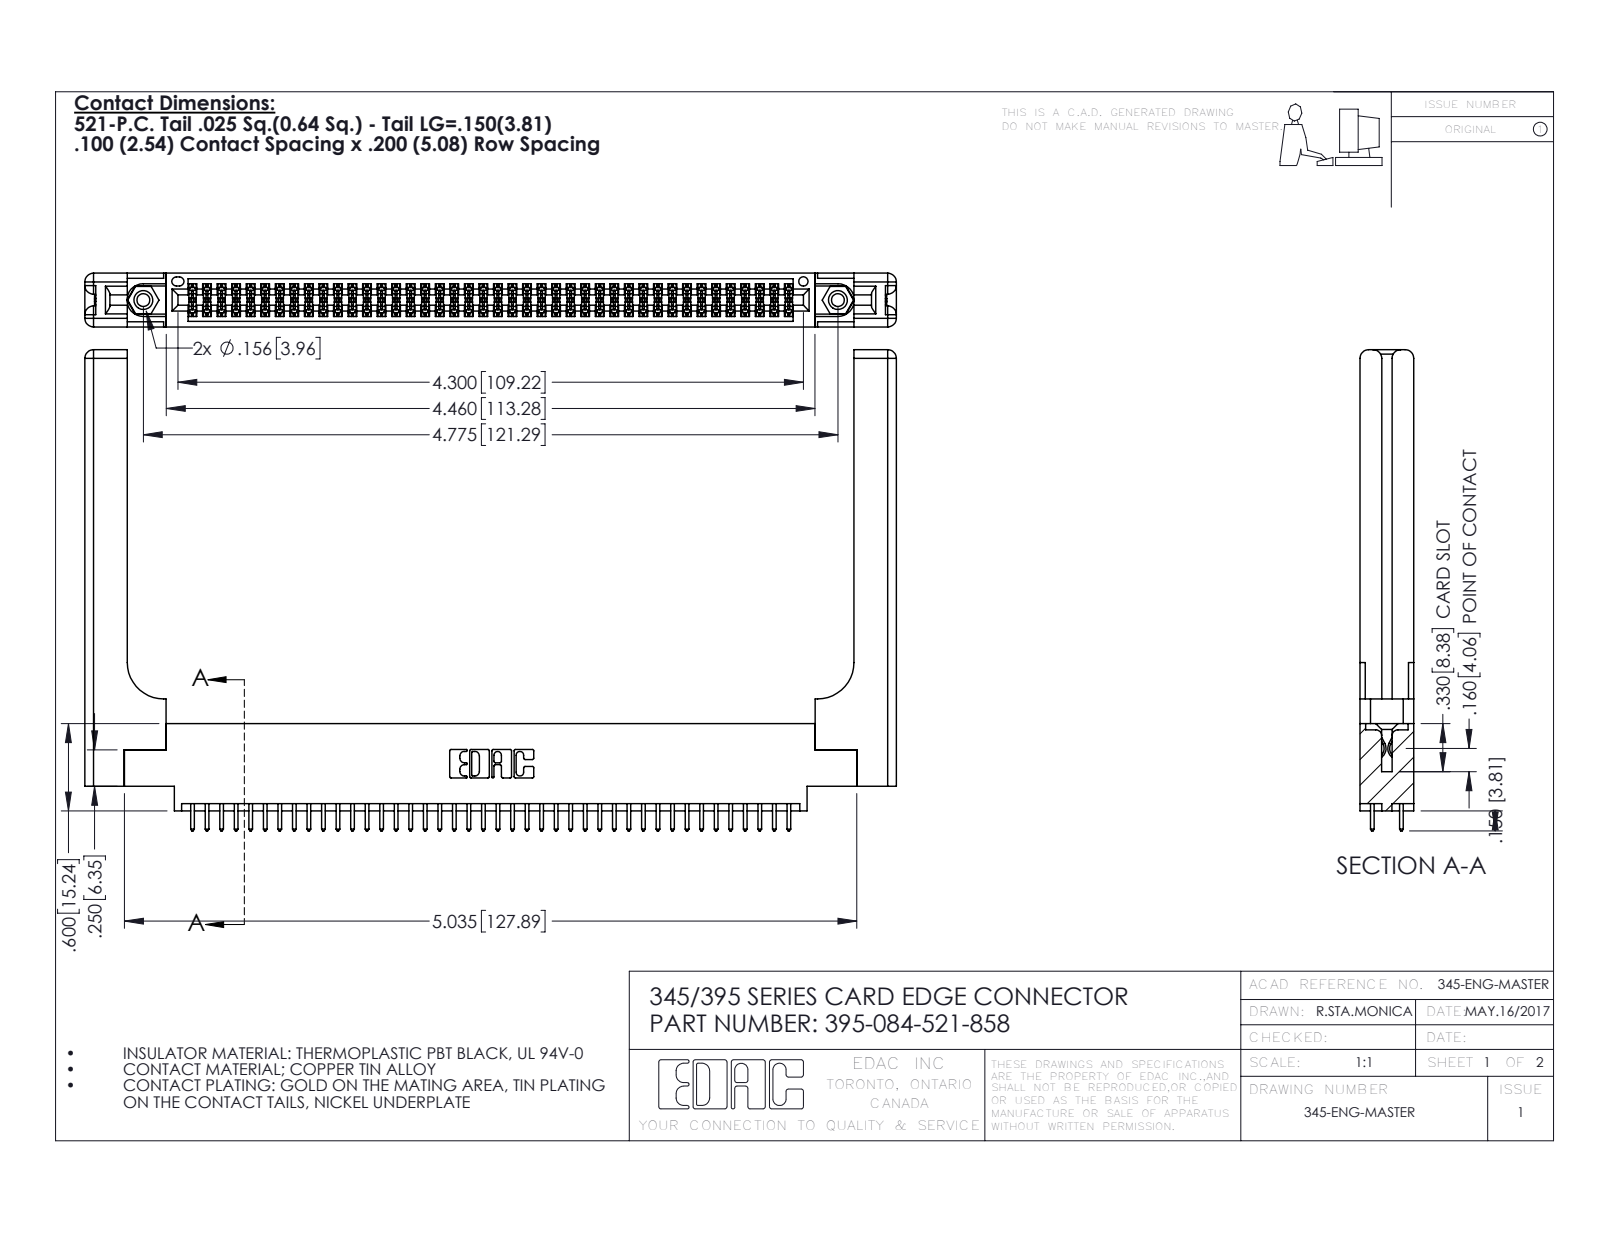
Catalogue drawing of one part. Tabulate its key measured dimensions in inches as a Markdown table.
| quantity | value |
| --- | --- |
| part name | 345-220-058_345-220-058; 345 Part_0.170 Offset - 0.156 Dia-TH; 345-250-001_345-250-001-102; 395-084-521-858 (+1 more) |
| STEP written by | SolidWorks 2016 (CONFIG_CONTROL_DESIGN) |
| units | inches |
| bodies | 89 solids, 4586 faces (3004 planar, 1522 cylindrical, 60 other) |
| overall size | 5.579 × 3.307 × 0.37 |
| volume | 1.348 in³ |
| surface area | 38.92 in² |
| round holes (diameter × count) | 0.089 × 2, 0.125 × 2, 0.156 × 2, 0.064 × 1 |
| round bosses / shafts (diameter × count) | 0.155 × 2 |
| partial cylindrical surfaces (radius × count) | 0.006 × 126, 0.01 × 84, 0.01 × 22, 0.06 × 16, 0.007 × 6, 0.031 × 6, 0.026 × 3, 0.014 × 2 |
| main face-to-face distances | 0.072, 0.37, 0.298, 0.098, 0.272, 0.025, 0.2, 0.225, 0.148, 0.15 |
| hole center spacings | 0.27, 4.539, 4.775 |
